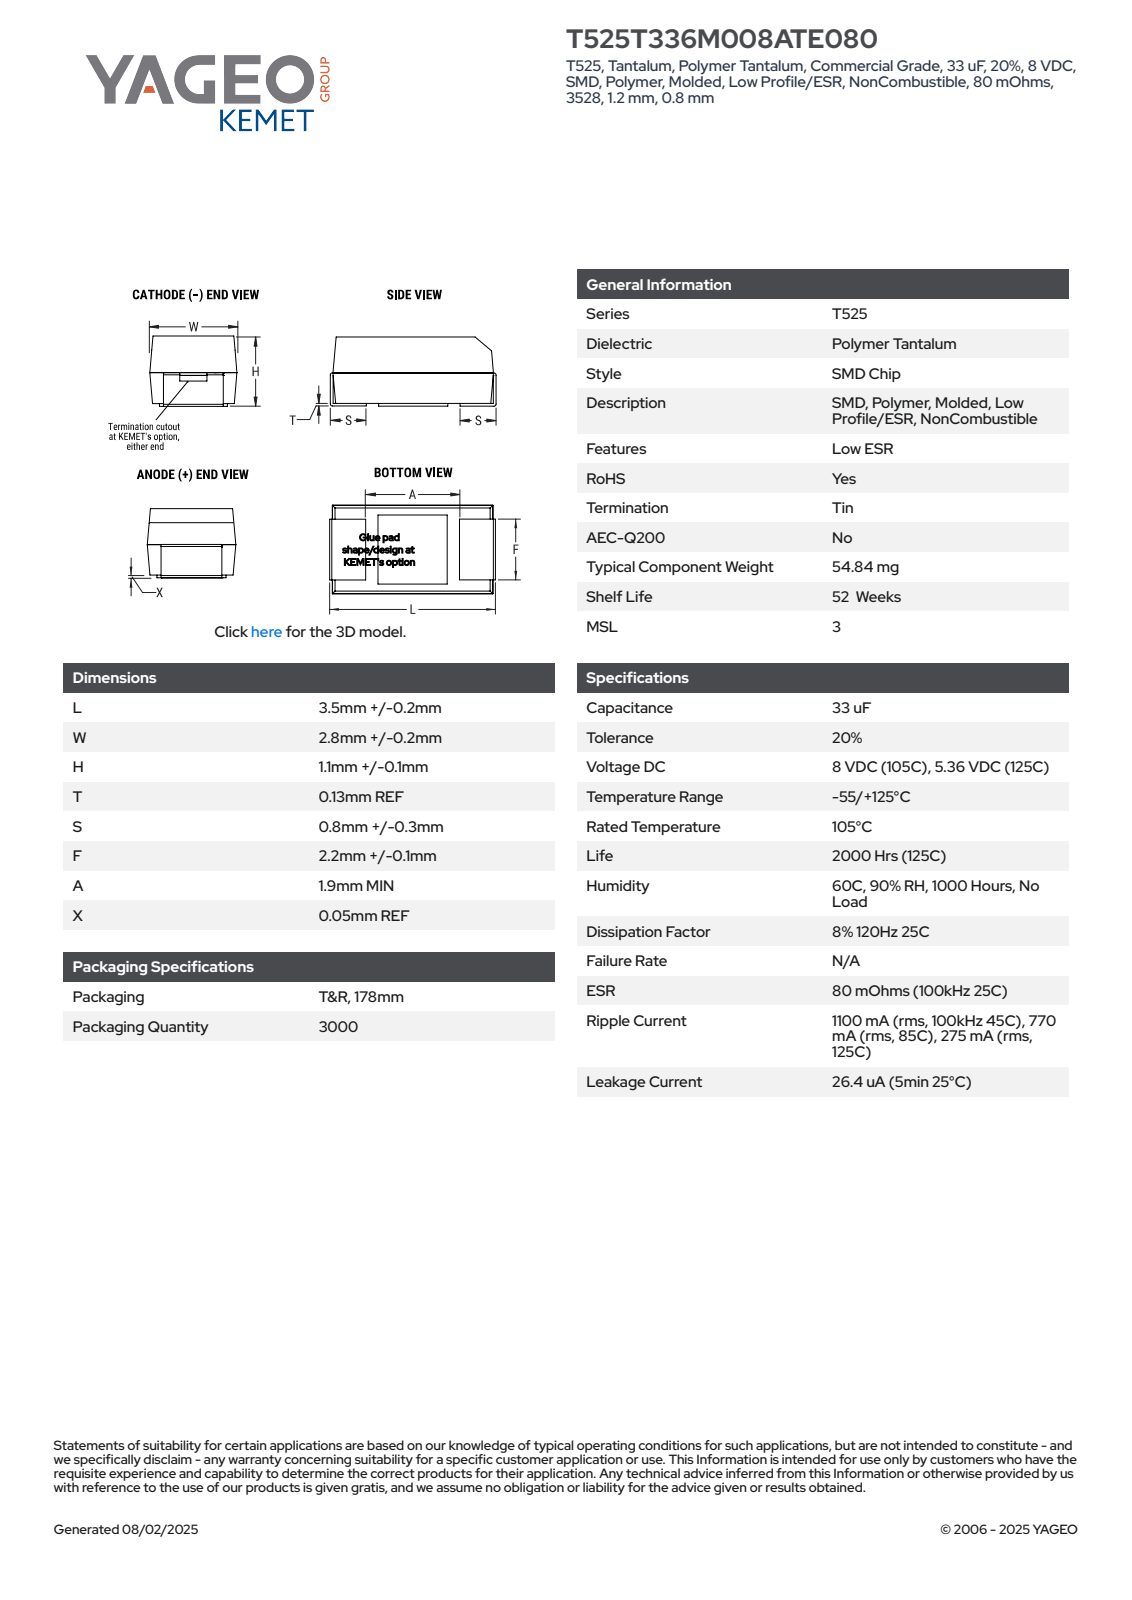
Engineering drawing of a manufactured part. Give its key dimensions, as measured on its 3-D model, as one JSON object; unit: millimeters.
{"part_name": "CTSM_TCM2NBKRPEG_3528_L3.7W3H1.2T0.13S0.8F2.3A1.9X0.05", "step_written_by": "SolidWorks 2014 (AUTOMOTIVE_DESIGN)", "units": "millimeters", "bodies": {"solids": 4, "faces": 90, "planar": 86, "cylindrical": 4, "other": 0}, "overall_size": [3.7, 3, 1.33], "volume_mm3": 12, "surface_area_mm2": 40, "partial_cylinders_radius": [[0.1, 4]], "face_to_face_distances": [1.2, 1.33, 3.57, 2.89, 2.88, 3.7, 3.44, 0.67, 0.8, 2.9]}
